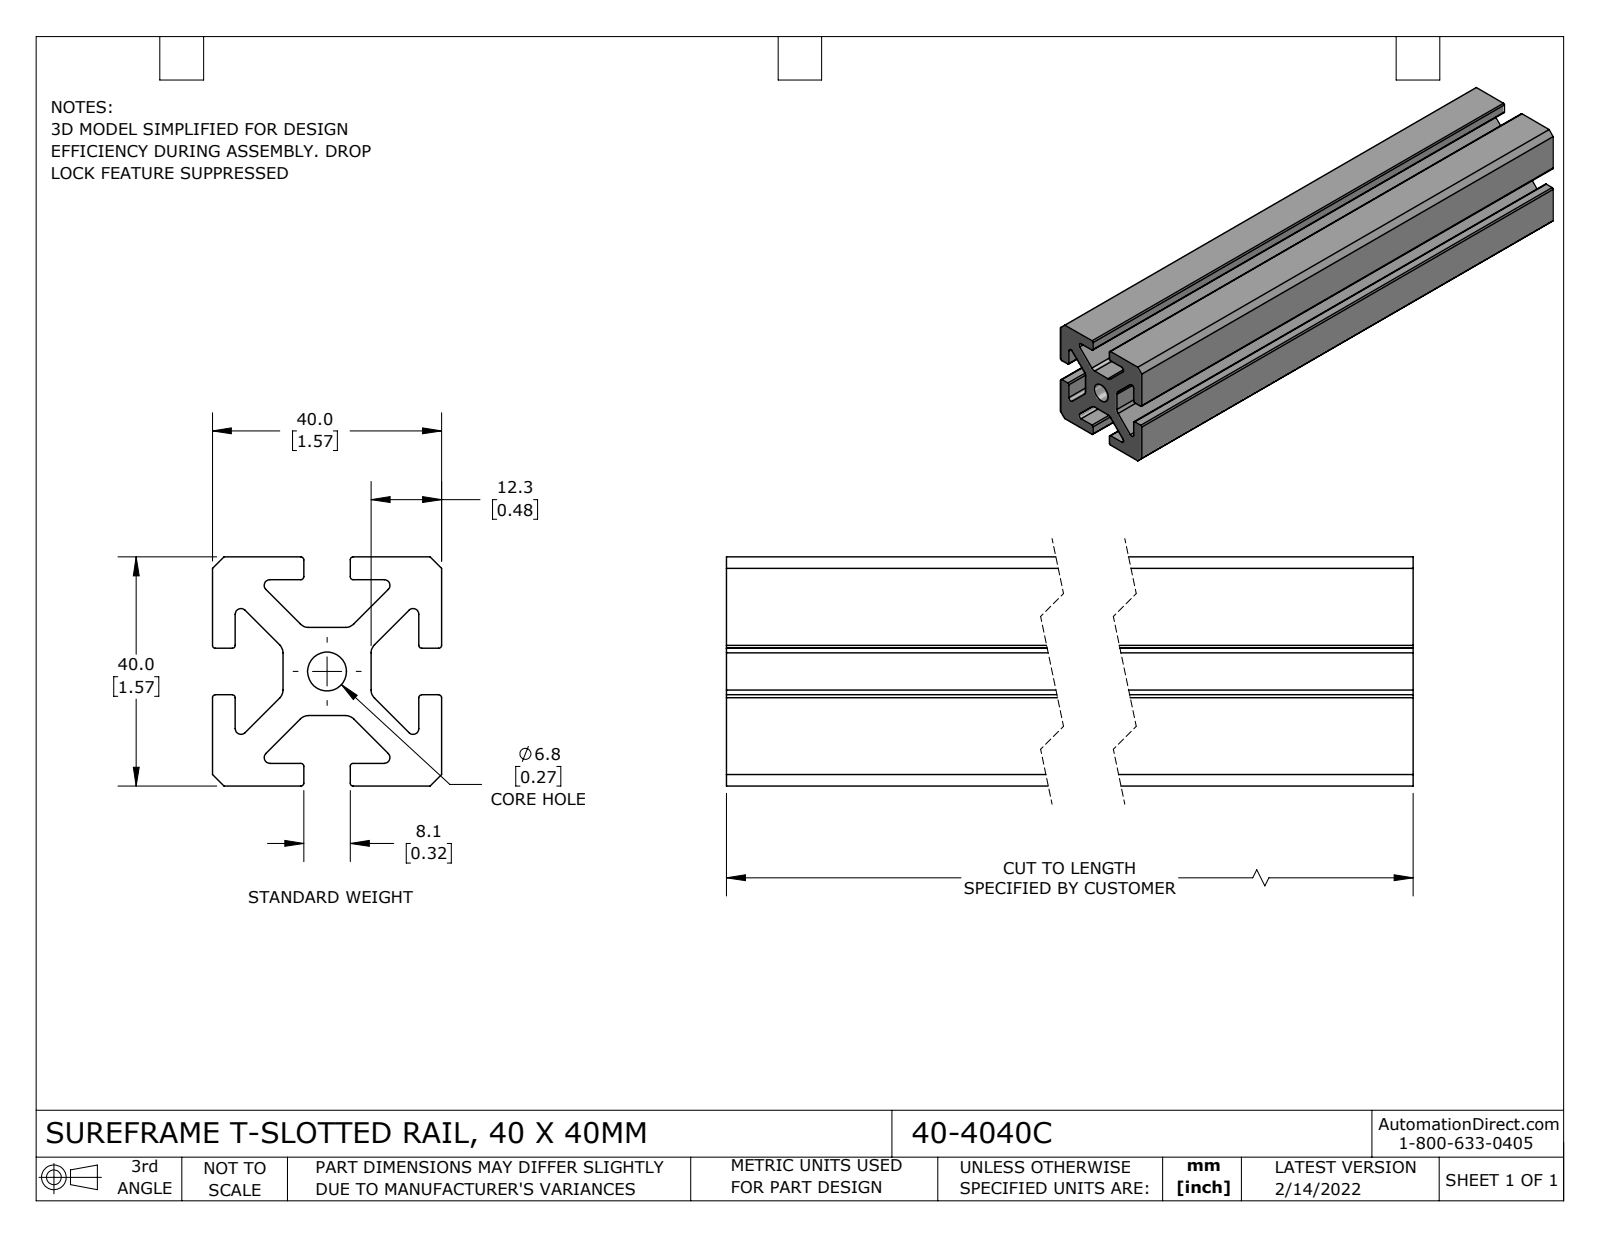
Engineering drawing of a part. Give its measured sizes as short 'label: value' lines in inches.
name: 40-4040C
written by: SolidWorks 2021 (CONFIG_CONTROL_DESIGN)
unit: in
bodies: 1 solid, 78 faces (42 planar, 36 cylindrical, 0 other)
size: 8 × 1.575 × 1.575
volume: 11 in³; area: 111.5 in²
holes: 1× ⌀0.268
rounds: 16× R0.02, 8× R0.039, 8× R0.079
face distances: 1.575, 0.156, 1.419, 0.202, 0.484, 1.091, 0.328, 0.934, 0.628, 0.947
